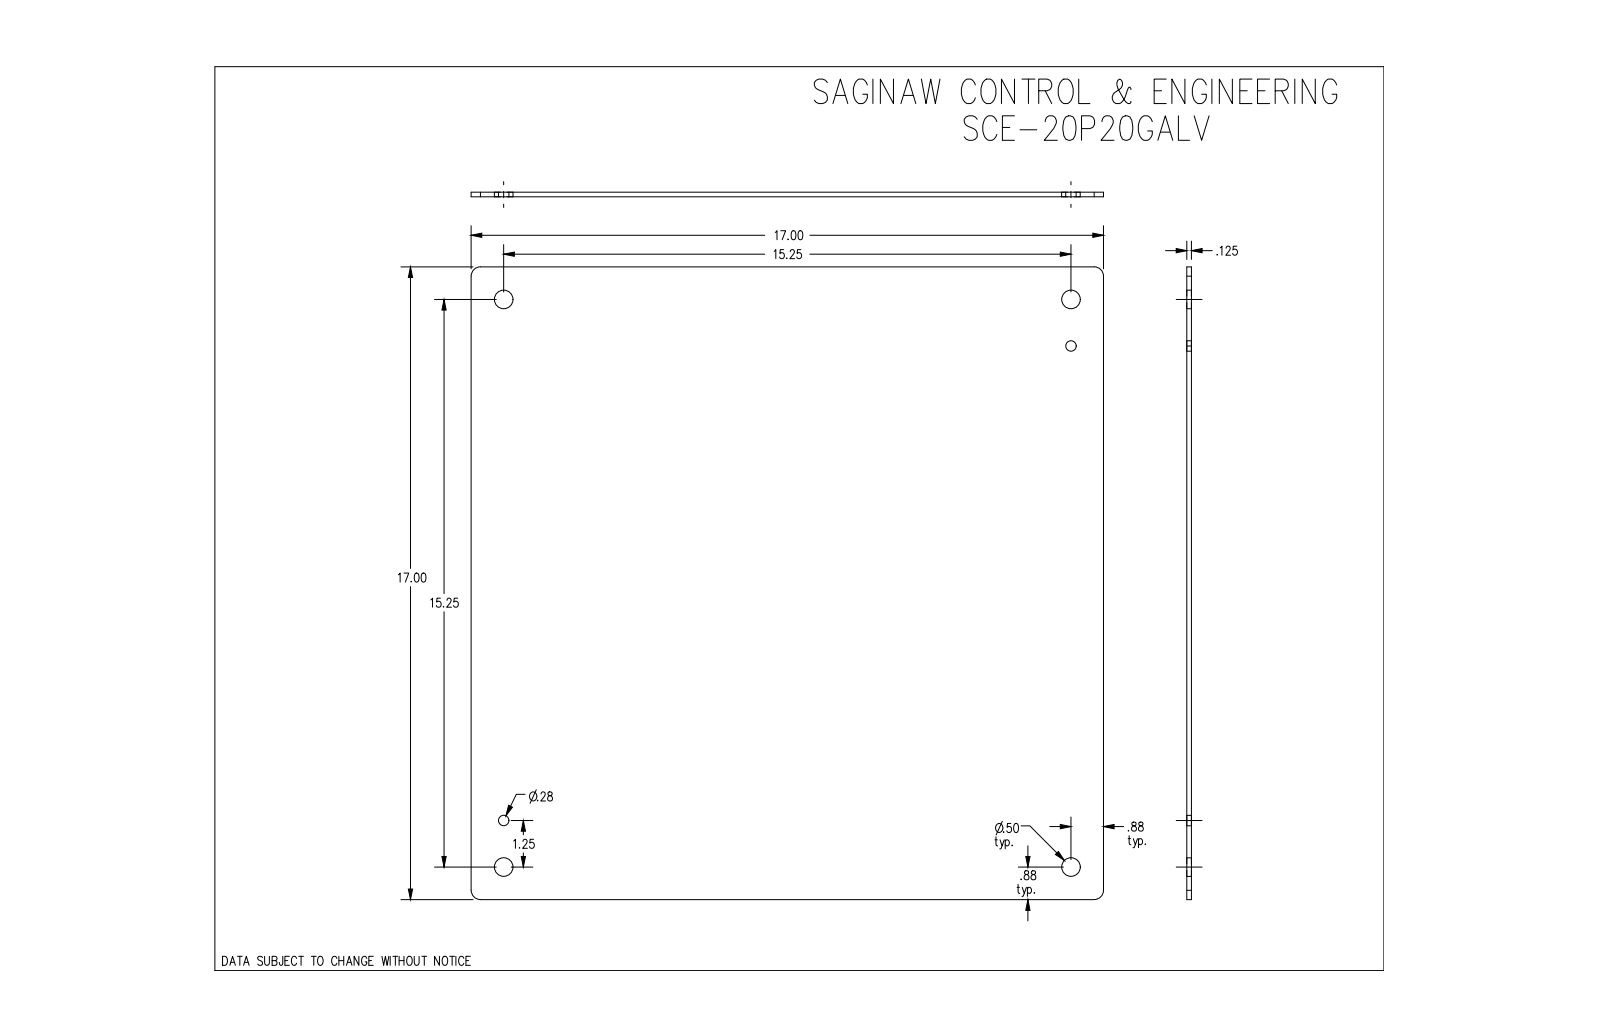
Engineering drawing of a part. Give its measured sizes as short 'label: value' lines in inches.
name: SCE-20P20GALV
written by: SolidWorks 2019 (CONFIG_CONTROL_DESIGN)
unit: in
bodies: 1 solid, 16 faces (6 planar, 10 cylindrical, 0 other)
size: 17 × 17 × 0.125
volume: 36 in³; area: 585.5 in²
holes: 4× ⌀0.5, 1× ⌀0.281, 1× ⌀0.281
rounds: 4× R0.25
face distances: 0.125, 17
hole spacings: 15.25, 1.25, 14, 15.301, 20.701, 21.566, 19.877
